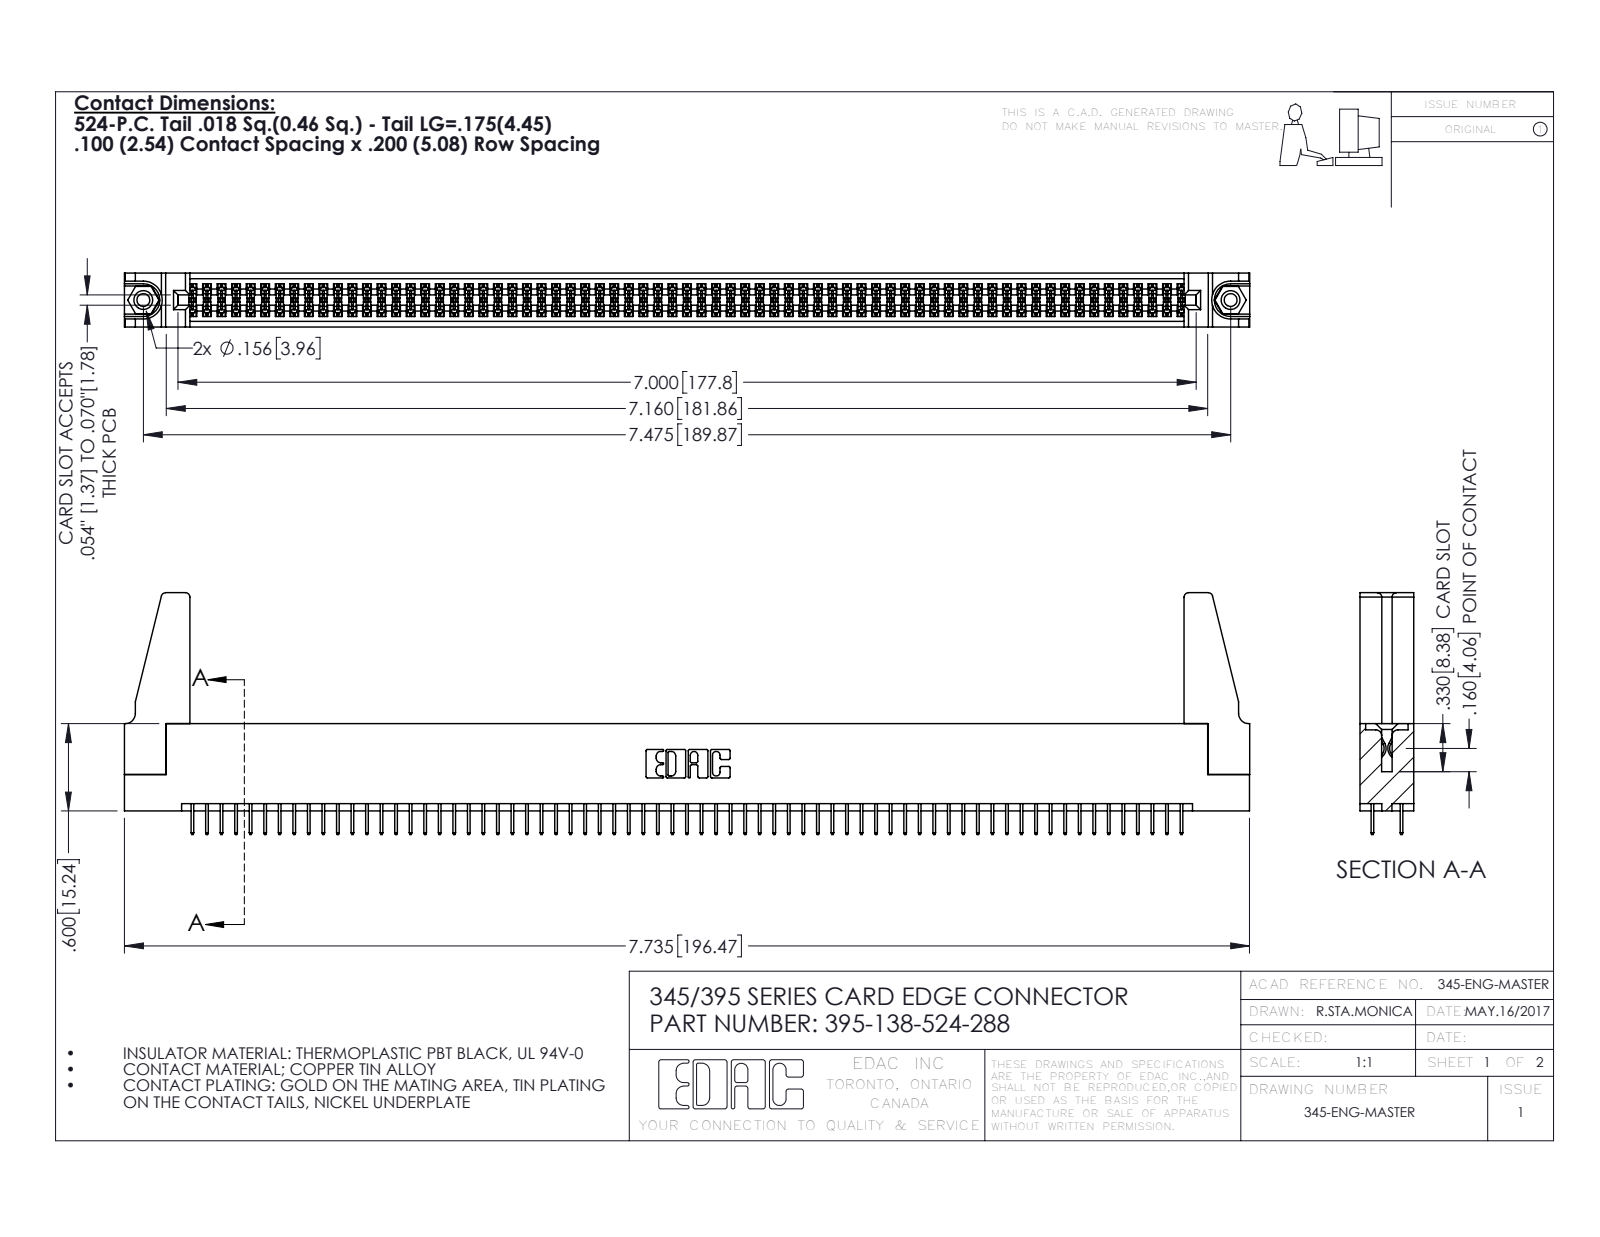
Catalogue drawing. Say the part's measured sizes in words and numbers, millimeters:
The part is named "345-250-001_345-250-001-102; 345 Part_Flush Mounting Lugs - 0.156 Dia-TH; 395-138-524-288; 345-292-001_345-293-124 (+1 more)". Its 3-D file was written by "SolidWorks 2016 (CONFIG_CONTROL_DESIGN)". It is 143 solids with 7702 faces: 5534 planar, 2152 cylindrical and 16 other. Overall it measures 196.5 by 42.2 by 9.4 millimeters. Its volume is 22 380 cubic millimeters and its surface area 31 370 square millimeters. Round holes: 2 of diameter 2.3, 2 of diameter 3.2, 2 of diameter 4, 1 of diameter 1.6. Round bosses or shafts: 2 of diameter 3.9. Partial cylindrical surfaces (rounded edges, fillets, slot ends): 207 of radius 0.2, 22 of radius 0.3, 8 of radius 0.8, 6 of radius 0.2, 6 of radius 0.8, 3 of radius 0.7, 2 of radius 0.4, 2 of radius 0.5. The main face-to-face distances are 1.8, 7.6, 9.4, 5.1, 2.5, 6.9, 0.6, 5.7, 1.8, 4.4. The hole center spacings are 6.9, 183.9, 189.9.
